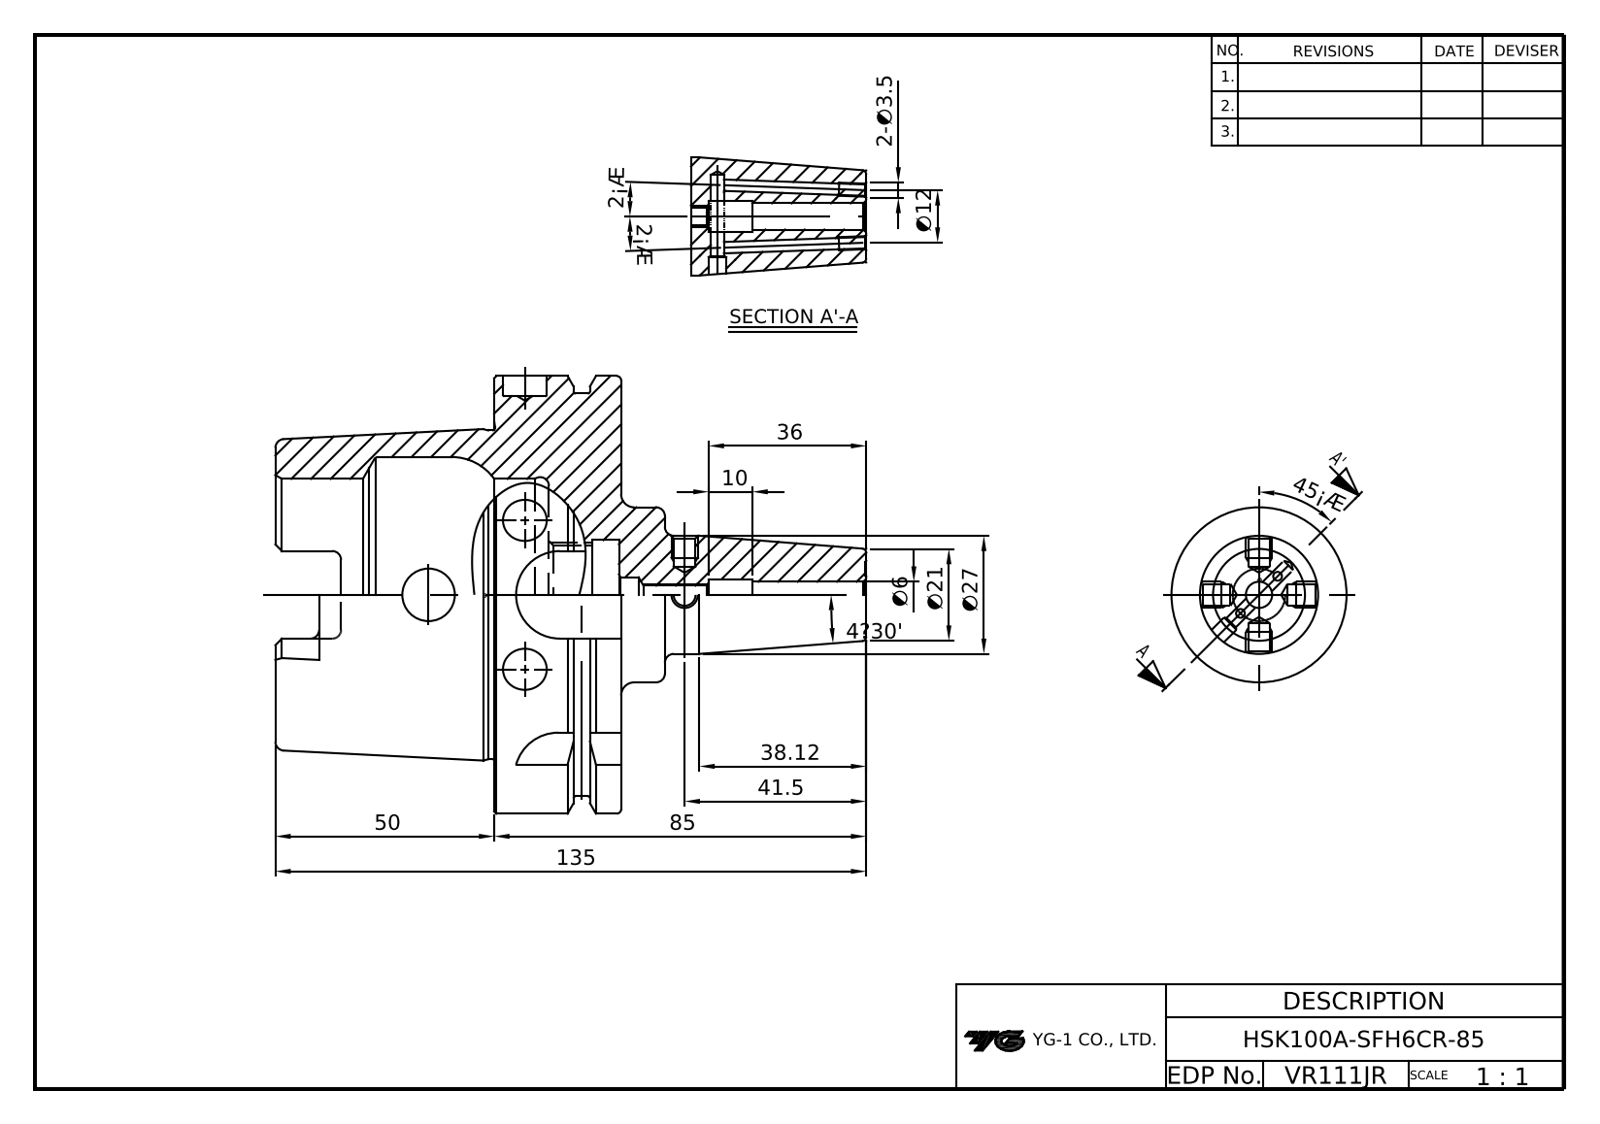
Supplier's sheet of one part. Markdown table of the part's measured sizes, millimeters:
| quantity | value |
| --- | --- |
| part name | LO-HSK100A-SFH6CR-85 |
| STEP written by | Autodesk Inventor 2024 (AUTOMOTIVE_DESIGN) |
| units | millimeters |
| bodies | 1 solid, 123 faces (39 planar, 37 cylindrical, 47 other) |
| overall size | 135 × 100 × 100 |
| volume | 287 030 mm³ |
| surface area | 55 412 mm² |
| round holes (diameter × count) | 2.46 × 2, 4.3 × 1, 6 × 1, 7.2 × 1, 10 × 1, 12 × 1, 22.38 × 1, 25 × 1, 53 × 1, 63 × 1 |
| round bosses / shafts (diameter × count) | 100 × 1, 92 × 1, 75.41 × 1, 40 × 1, 27 × 1 |
| partial cylindrical surfaces (radius × count) | 2 × 6, 4.88 × 4, 10 × 4 |
| main face-to-face distances | 29, 12.5, 16.5, 62.5, 79, 50, 10, 78.5, 28.5, 16 |
